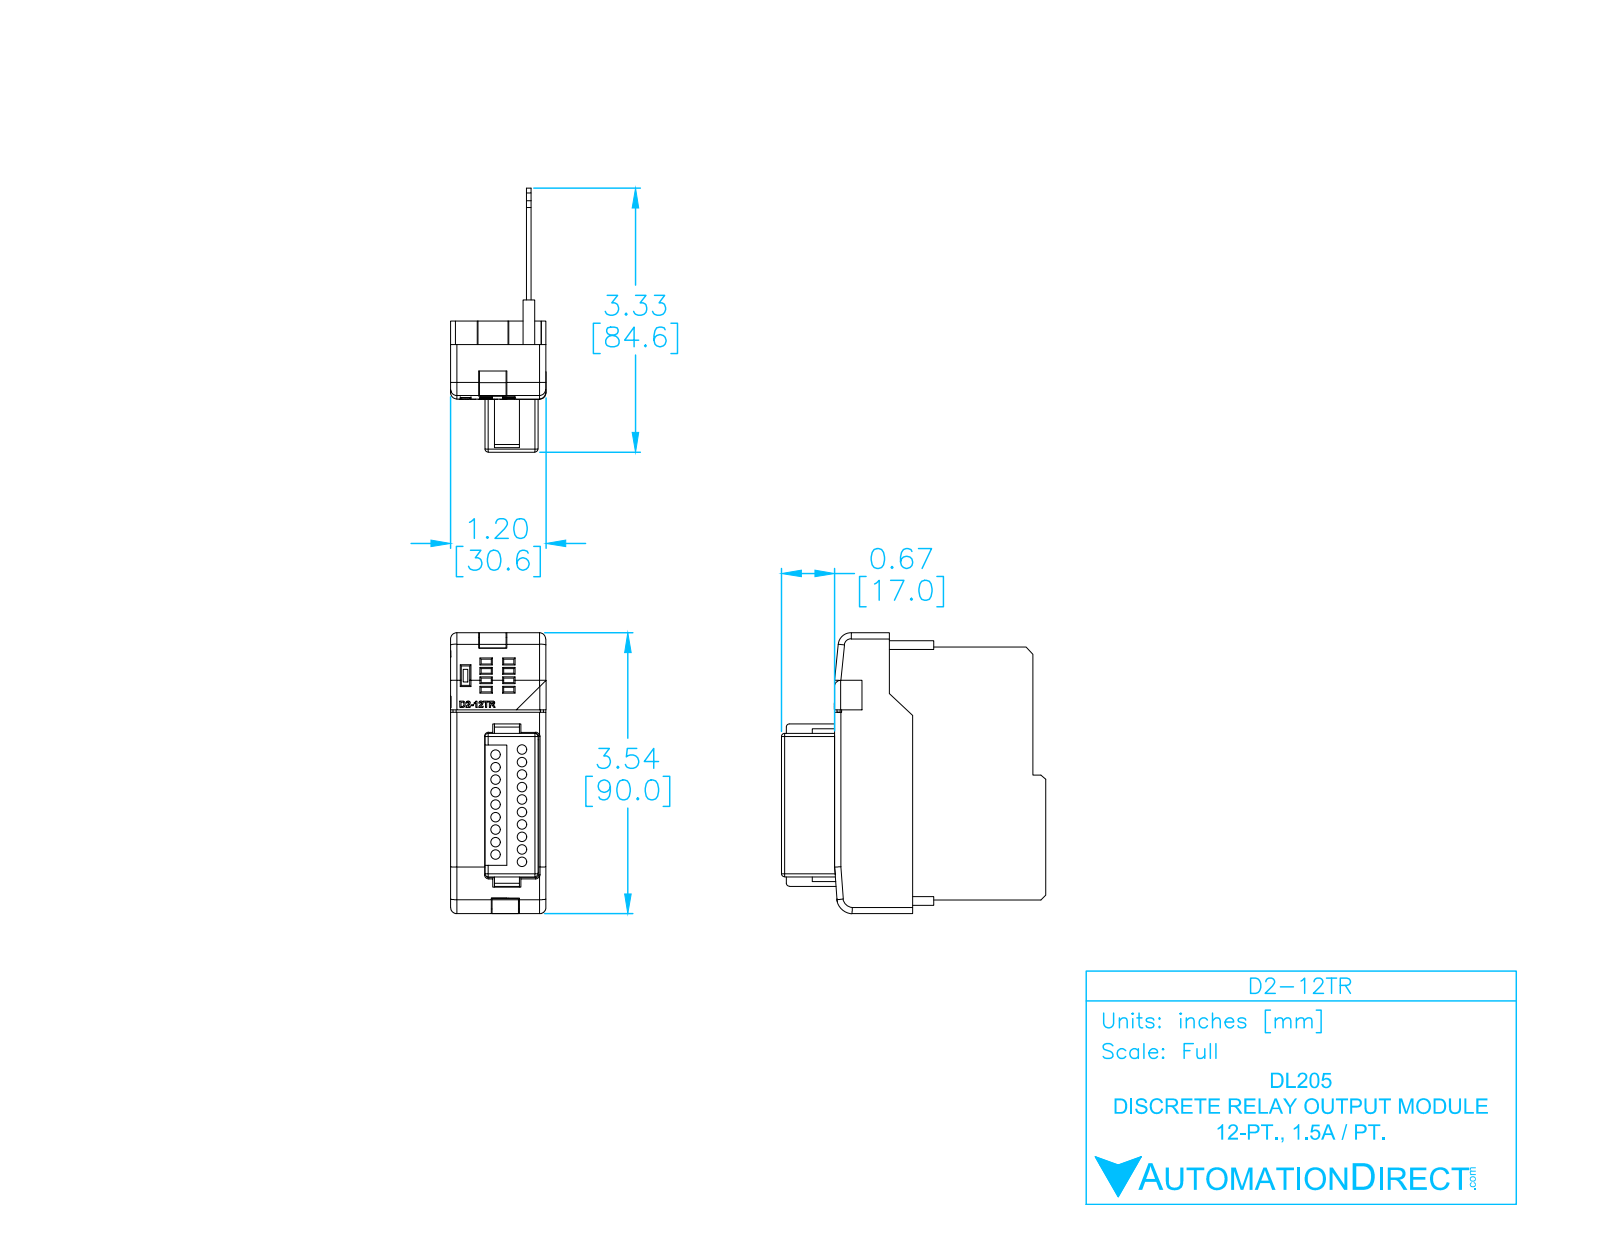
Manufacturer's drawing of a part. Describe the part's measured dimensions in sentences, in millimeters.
The part is named "D2-12TR_ModuleCase Light_NEW". Its 3-D file was written by "SolidWorks 2009 (AUTOMOTIVE_DESIGN)". It is 2 solids with 617 faces: 403 planar, 158 cylindrical and 56 other. Overall it measures 90 by 84.6 by 30.55 millimeters. Its volume is 30 556 cubic millimeters and its surface area 32 607 square millimeters. Round holes: 19 of diameter 3. Partial cylindrical surfaces (rounded edges, fillets, slot ends): 28 of radius 0.35, 18 of radius 1, 12 of radius 0.5, 11 of radius 2, 6 of radius 0.25, 1 of radius 2.62, 1 of radius 3.79, 1 of radius 4.12. The main face-to-face distances are 1.5, 4.72, 3.22, 6.22, 0.5, 1, 24.28, 29, 18, 11. The hole center spacings are 4, 8, 12, 16, 8.61, 8.77, 20, 10.16.
